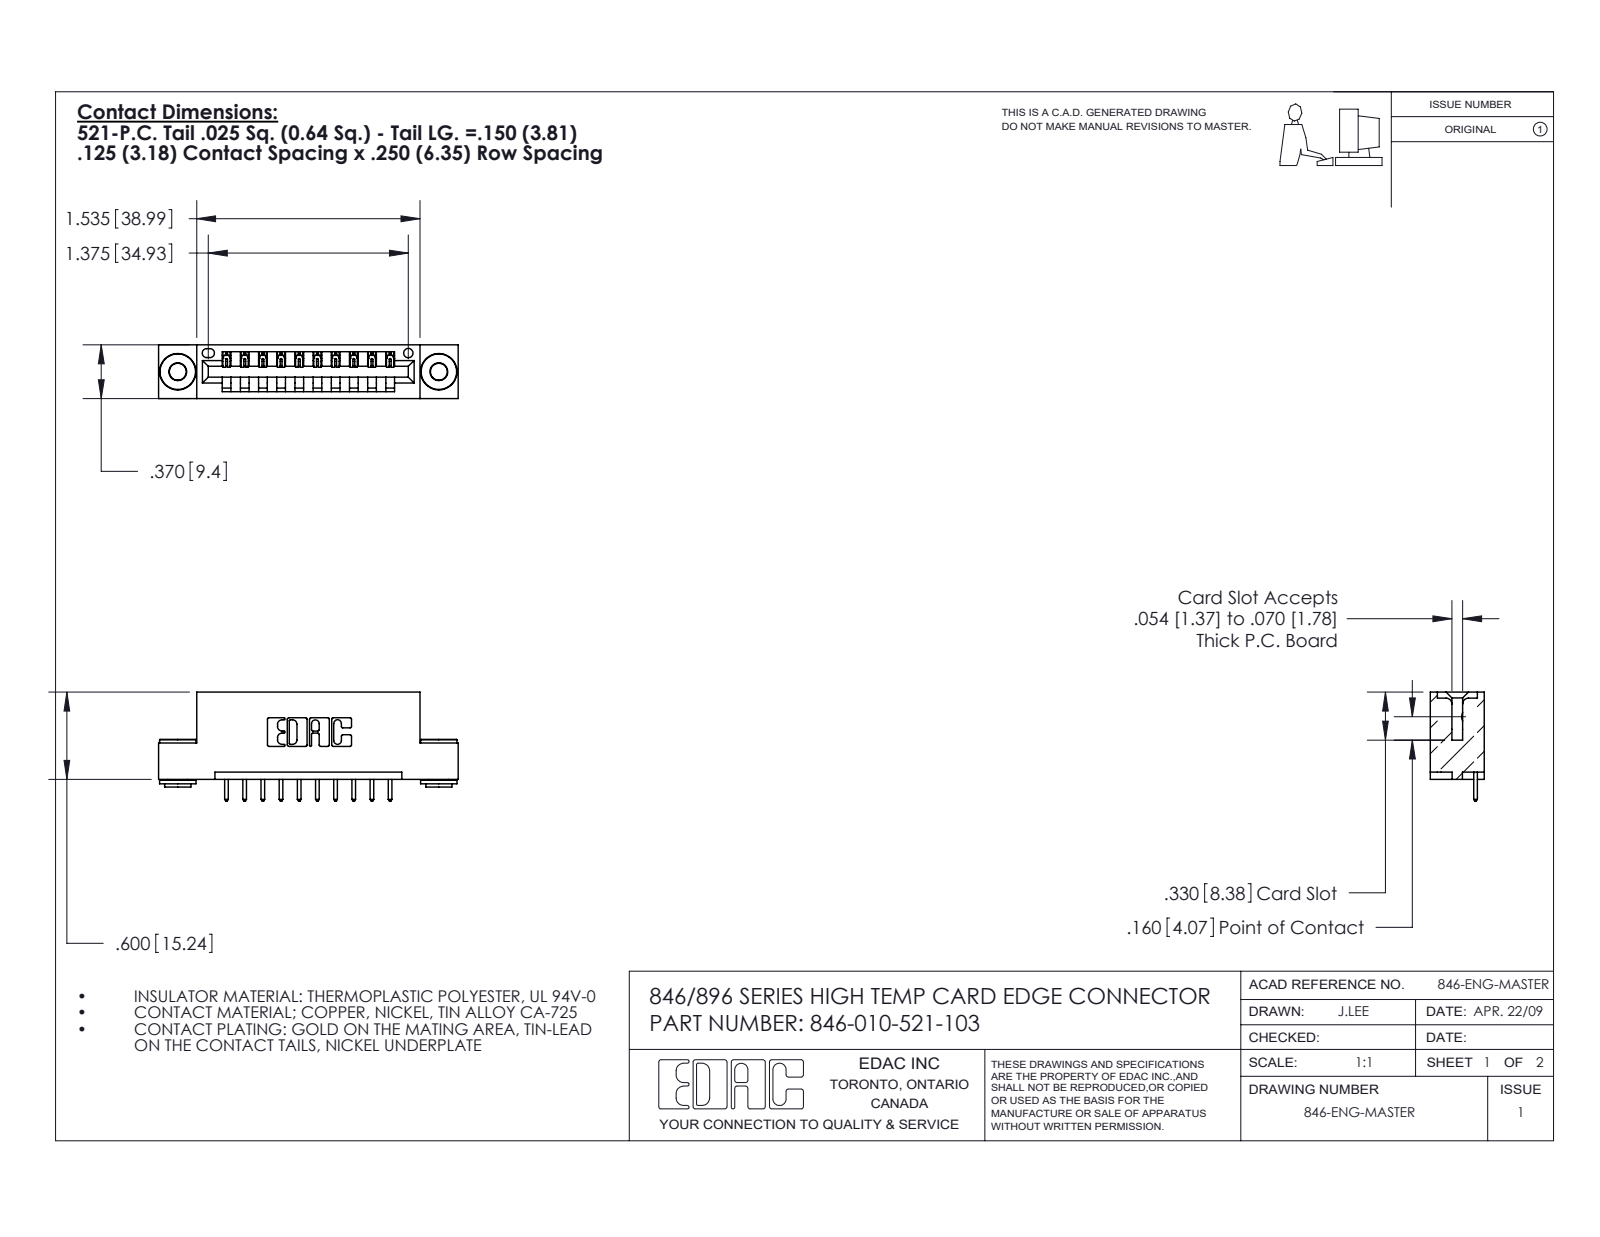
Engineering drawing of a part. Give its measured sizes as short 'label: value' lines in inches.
name: 346 Part_Flush Mounting Lugs - 0.156 Dia-TH; 346-010-521-103; 345-250-002_345-250-002-102; 345-292-001_345-293-121
written by: SolidWorks 2016 (CONFIG_CONTROL_DESIGN)
unit: in
bodies: 13 solids, 740 faces (486 planar, 246 cylindrical, 8 other)
size: 2.06 × 0.75 × 0.37
volume: 0.292 in³; area: 8.888 in²
holes: 2× ⌀0.116, 2× ⌀0.156, 1× ⌀0.064
bosses: 2× ⌀0.25, 2× ⌀0.18, 2× ⌀0.136
rounds: 22× R0.01, 20× R0.006, 20× R0.01, 6× R0.007, 6× R0.031, 3× R0.026, 2× R0.031, 2× R0.04
face distances: 0.25, 0.37, 0.048, 0.322, 0.025, 0.148, 0.222, 0.1, 0.174, 0.072
hole spacings: 0.246, 1.59, 1.795
